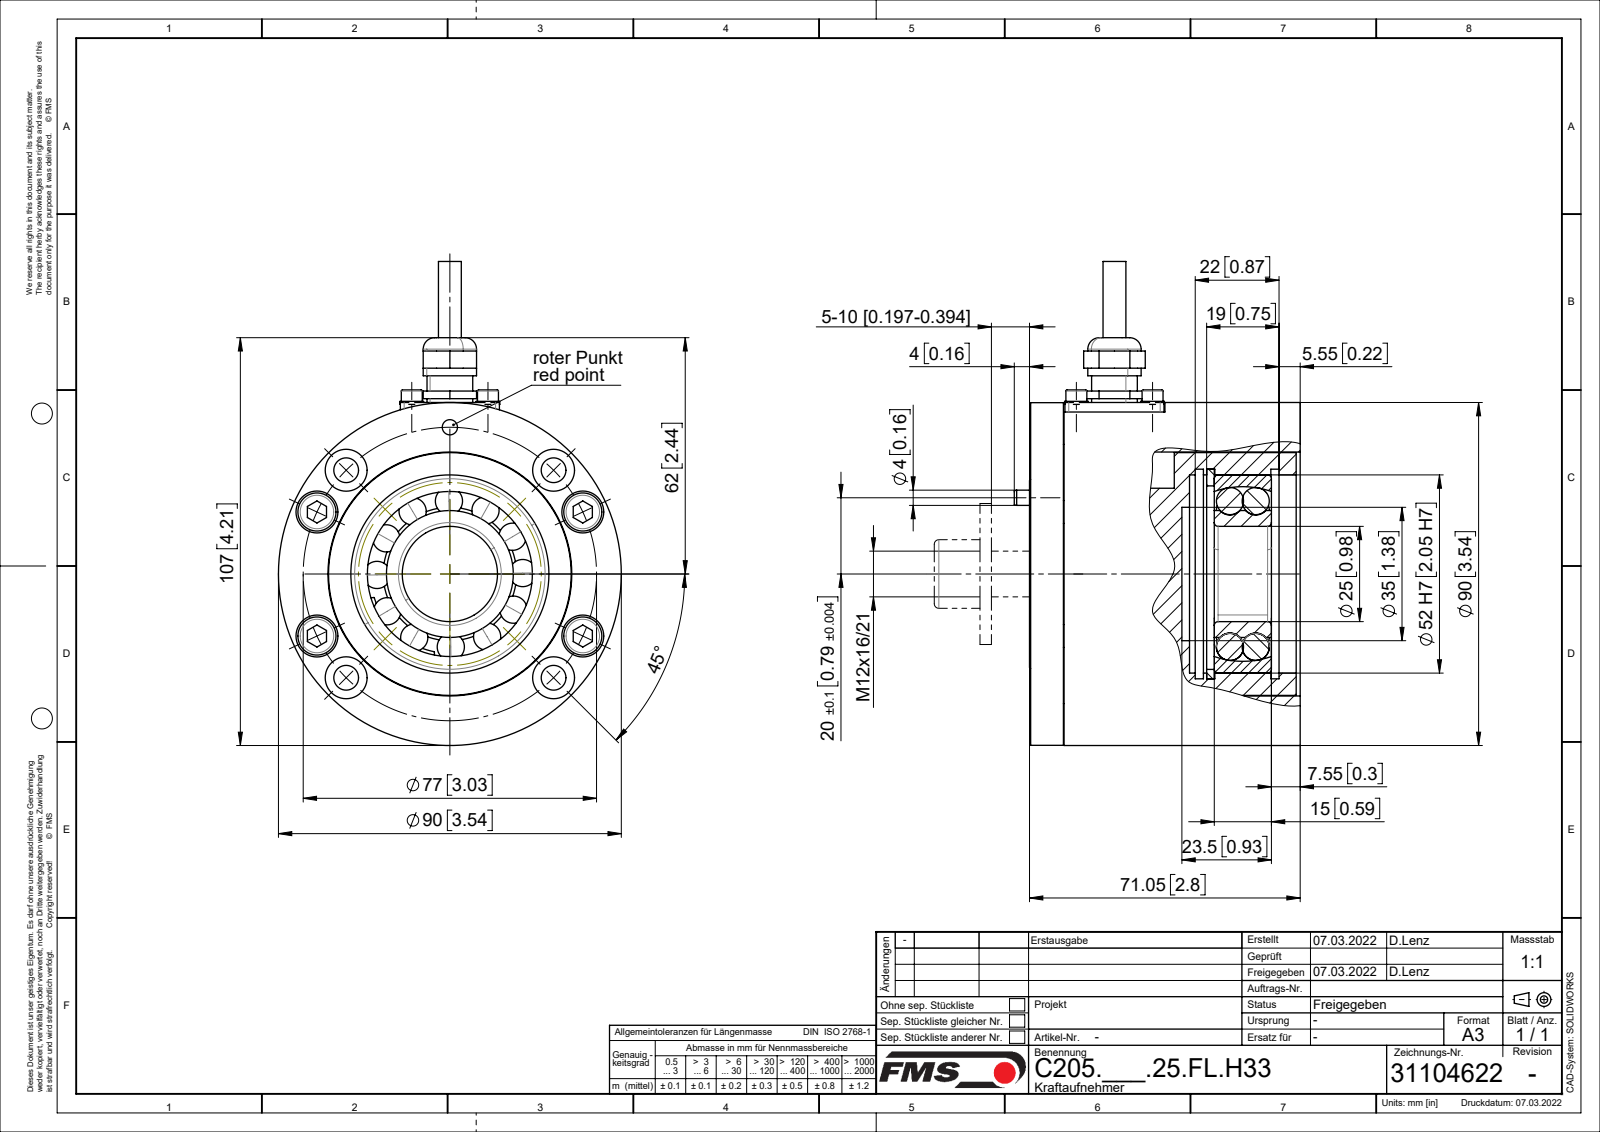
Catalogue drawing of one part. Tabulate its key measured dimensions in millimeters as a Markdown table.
| quantity | value |
| --- | --- |
| part name | 31104484_Stp_01; Zyl-Schr DIN912_M12x25; Zyl-Schr DIN912_M3x6; Spannstift_ISO13337_D04x10 (+8 more) |
| STEP written by | SolidWorks 2018 (CONFIG_CONTROL_DESIGN) |
| units | millimeters |
| bodies | 48 solids, 577 faces (201 planar, 230 cylindrical, 146 other) |
| overall size | 127 × 96.05 × 90 |
| volume | 310 171 mm³ |
| surface area | 122 941 mm² |
| round holes (diameter × count) | 6.5 × 8, 11 × 8, 2.5 × 6, 3.1 × 4, 3.4 × 4, 5 × 4, 7 × 4, 4 × 2, 3 × 1, 6 × 1, 10.2 × 1, 12.2 × 1 |
| round bosses / shafts (diameter × count) | 10 × 4, 6.2 × 4, 6 × 4, 5.5 × 4, 3 × 4, 12 × 2, 90 × 1, 89.9 × 1 |
| partial cylindrical surfaces (radius × count) | 0.1 × 4, 1 × 4, 0.5 × 2, 4.24 × 2, 5 × 2, 20.8 × 1, 24.1 × 1 |
| main face-to-face distances | 6, 6.5, 32, 25.5, 2, 33.05, 38, 8.6, 29.1, 37.7 |
| hole center spacings | 20, 38.5, 13.37, 14.14, 38.49, 44.16, 54.44, 63.07 |
